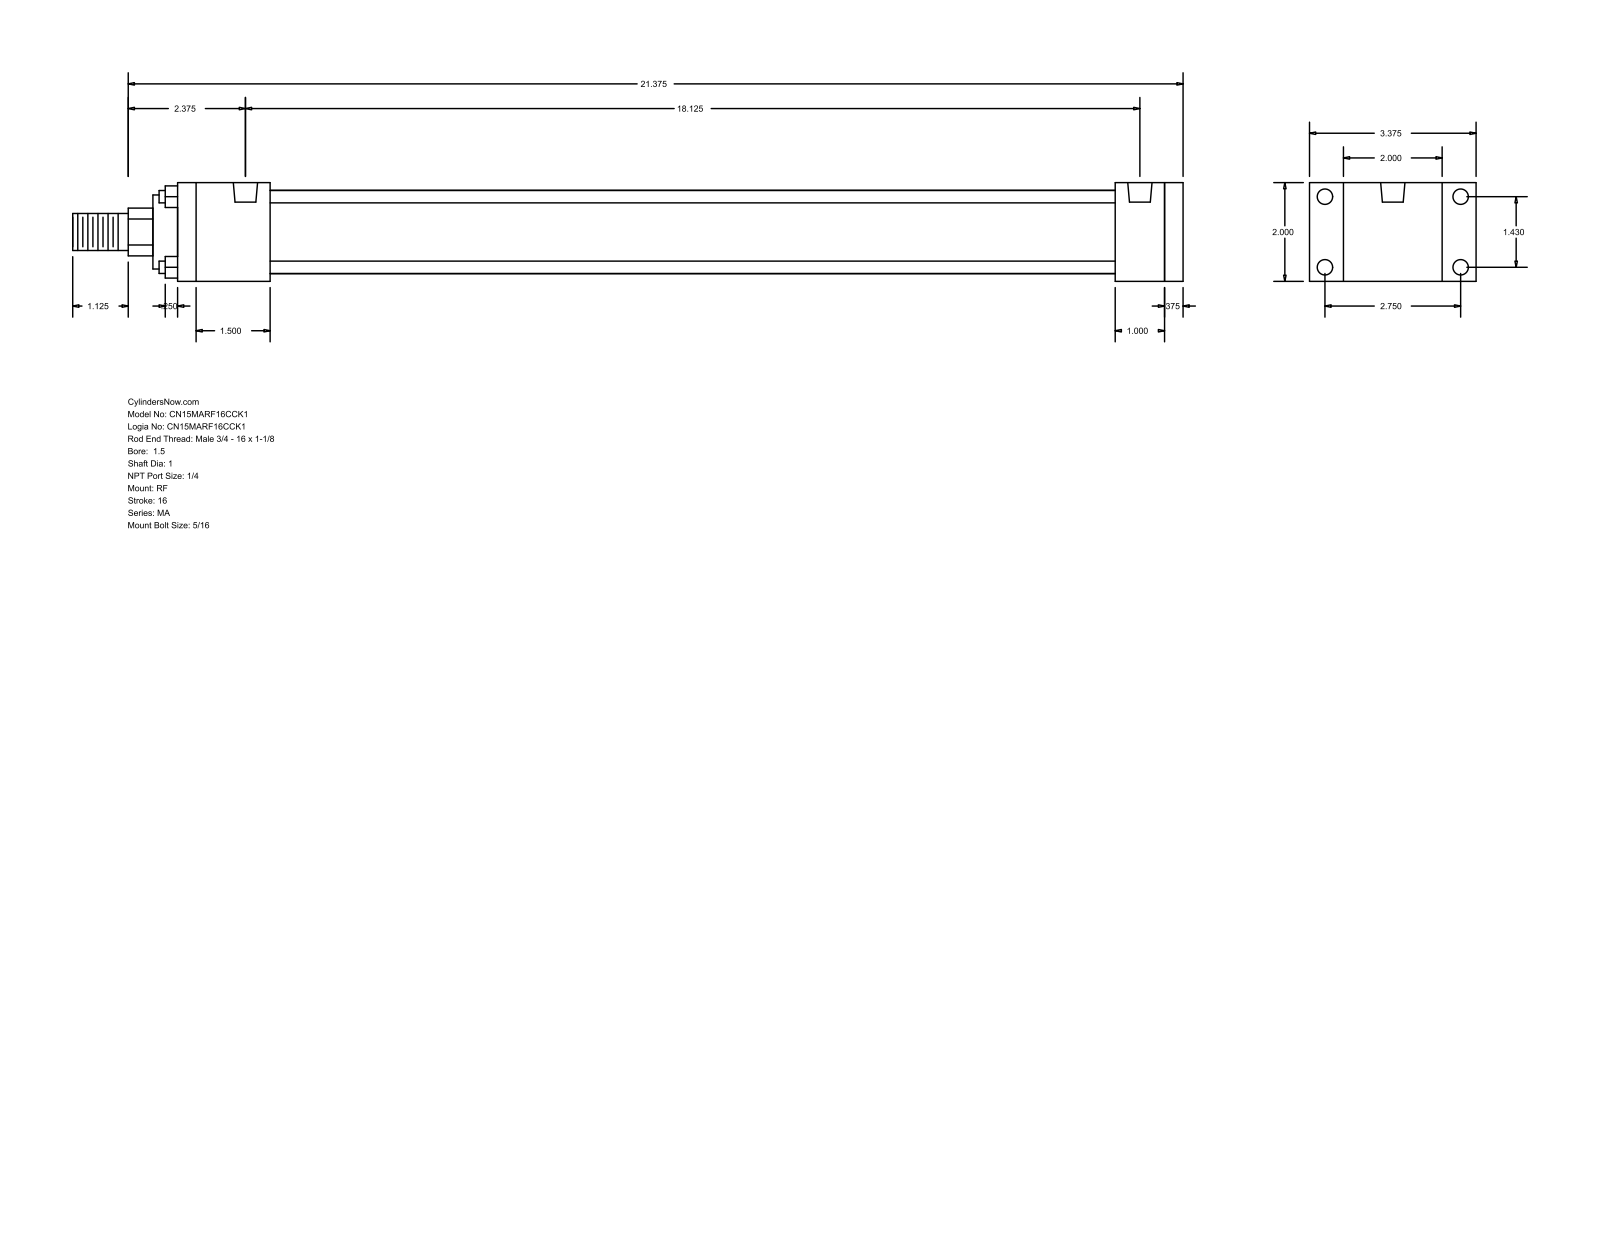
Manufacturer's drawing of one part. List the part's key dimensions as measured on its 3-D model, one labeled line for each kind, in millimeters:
Part name (STEP PRODUCT): MA_RF__0150_1
STEP written by: GSSL Pune (CONFIG_CONTROL_DESIGN)
Units: millimetres
Bodies: 0 solids, 92 faces (64 planar, 28 cylindrical, 0 other)
Overall size (bounding box): 571.5 × 85.72 × 50.8
Round holes (diameter × count): ⌀7.94 ×8, ⌀12.49 ×2
Round bosses / shafts (diameter × count): ⌀6.35 ×4, ⌀42.93 ×1, ⌀38.1 ×1, ⌀25.4 ×1, ⌀19.05 ×1
Partial cylindrical surfaces — rounded edges, fillets, slot ends (radius × count): R12.29 ×1
Main face-to-face distances: 50.8, 9.52, 517.52, 508, 25.4, 482.6, 34.92, 47.63, 434.97, 460.37
Hole centre spacings: 36.32, 69.84, 78.72, 460.37
